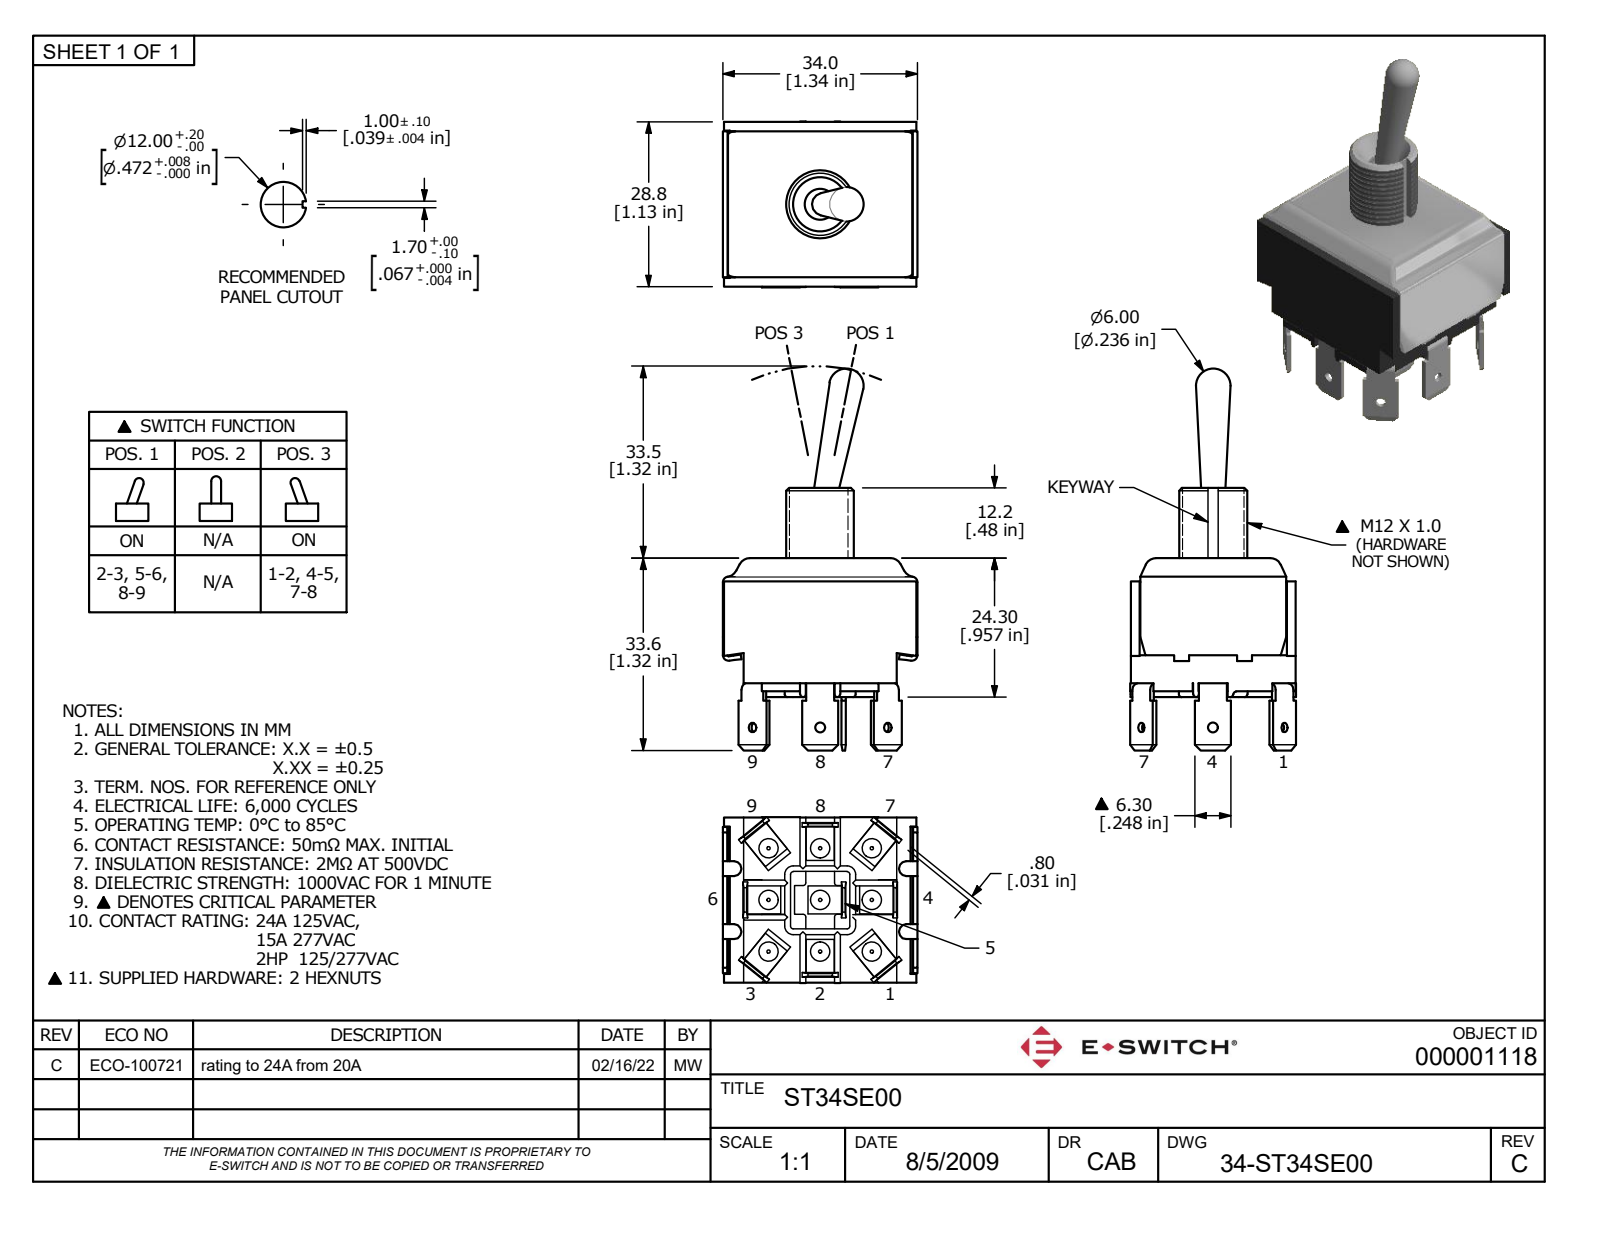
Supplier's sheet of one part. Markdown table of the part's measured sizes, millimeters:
| quantity | value |
| --- | --- |
| part name | ST34SE00 |
| STEP written by | Autodesk Inventor 2022 (AUTOMOTIVE_DESIGN) |
| units | millimeters |
| bodies | 1 solid, 456 faces (306 planar, 87 cylindrical, 63 other) |
| overall size | 66.66 × 34 × 28.96 |
| volume | 21 921 mm³ |
| surface area | 9 063 mm² |
| round holes (diameter × count) | 2 × 9, 1.7 × 6, 5.4 × 1 |
| round bosses / shafts (diameter × count) | 11.91 × 1 |
| partial cylindrical surfaces (radius × count) | 0.5 × 16, 0.3 × 9, 1.1 × 9, 1.75 × 6, 0.6 × 4, 1.3 × 4, 1.5 × 4, 0.2 × 2 |
| main face-to-face distances | 0.8, 1.2, 0.4, 32.8, 33.2, 32, 28.8, 3.65, 30.35, 2.85 |
| hole center spacings | 9, 12.73, 20.12, 18, 2.66, 12.69, 12.76, 25.46 |
